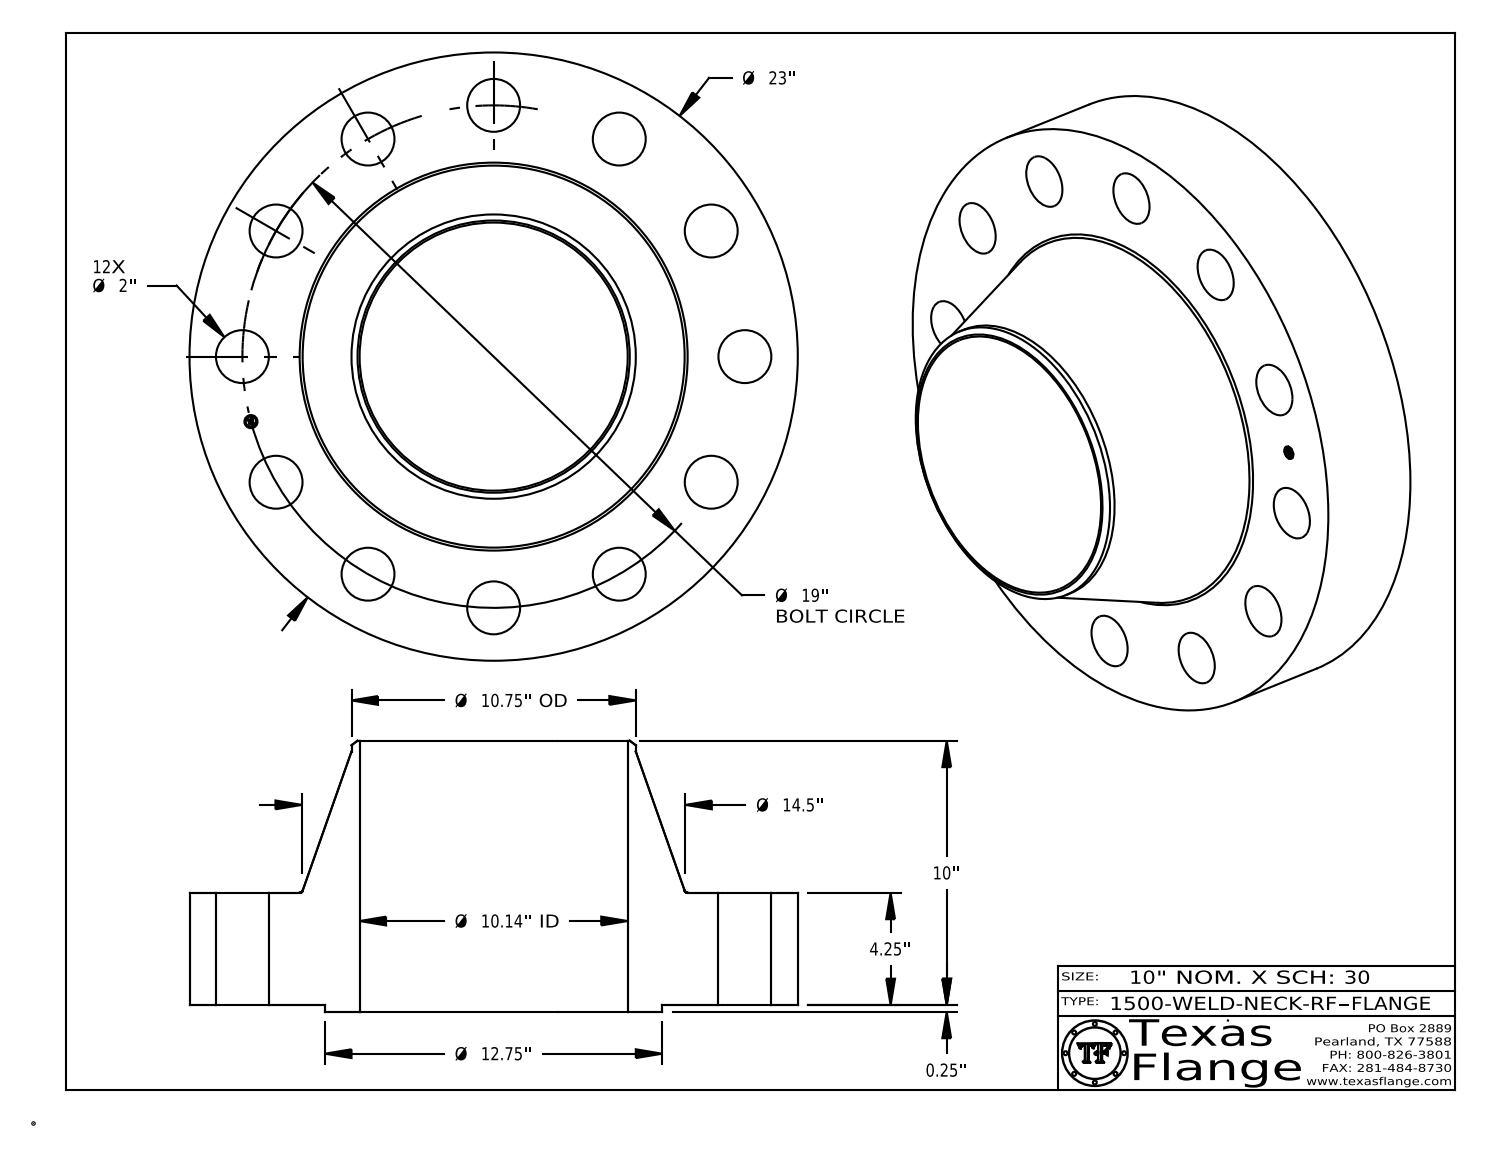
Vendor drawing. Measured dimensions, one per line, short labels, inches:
name: 1500-WELD-NECK-RF
written by: CATIA V5 STEP AP214 (AUTOMOTIVE_DESIGN)
unit: in
bodies: 1 solid, 427 faces (369 planar, 52 cylindrical, 6 other)
size: 23 × 23 × 10.25
volume: 1 520 in³; area: 1 717 in²
holes: 12× ⌀2, 1× ⌀0.495, 1× ⌀10.136
bosses: 8× ⌀0.03, 1× ⌀23, 1× ⌀12.75, 1× ⌀10.75, 1× ⌀0.39
face distances: 4.25, 0.25, 4.5, 10.25, 10, 5.75, 4.485, 4.235, 0.015, 5.765
hole spacings: 9.5, 13.435, 16.454, 18.352, 4.918, 19, 4.917, 15.074
